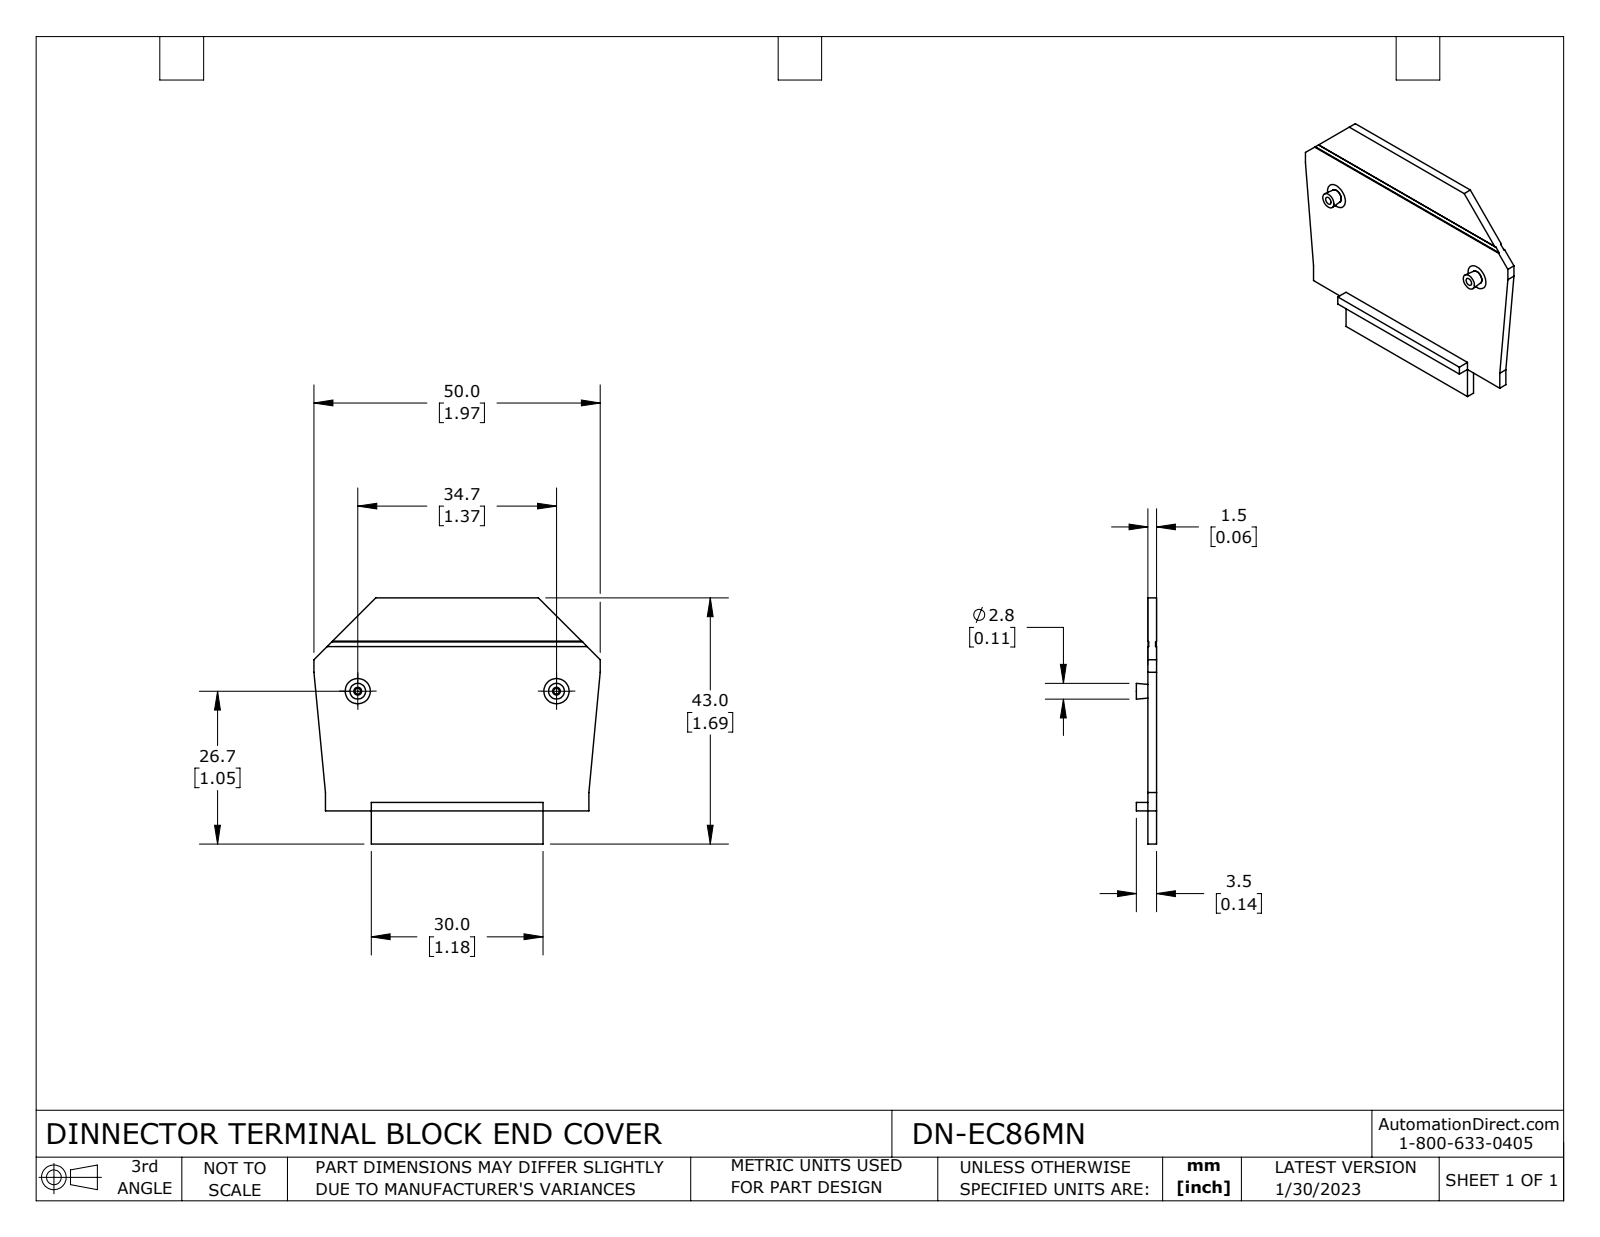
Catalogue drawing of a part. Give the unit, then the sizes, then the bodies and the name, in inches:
Units: inches
Overall size (bounding box): 1.969 × 1.693 × 0.138
Main face-to-face distances: 0.059, 0.053, 0.079, 0.138, 0.228, 0.287, 1.693, 1.465, 1.406, 0.132
Volume: 0.176 in³ · Surface area: 6.489 in²
Bodies: 1 solid, 50 faces (34 planar, 0 cylindrical, 16 other)
Part name (STEP PRODUCT): DN-EC86MN
STEP written by: SolidWorks 2021 (CONFIG_CONTROL_DESIGN)
